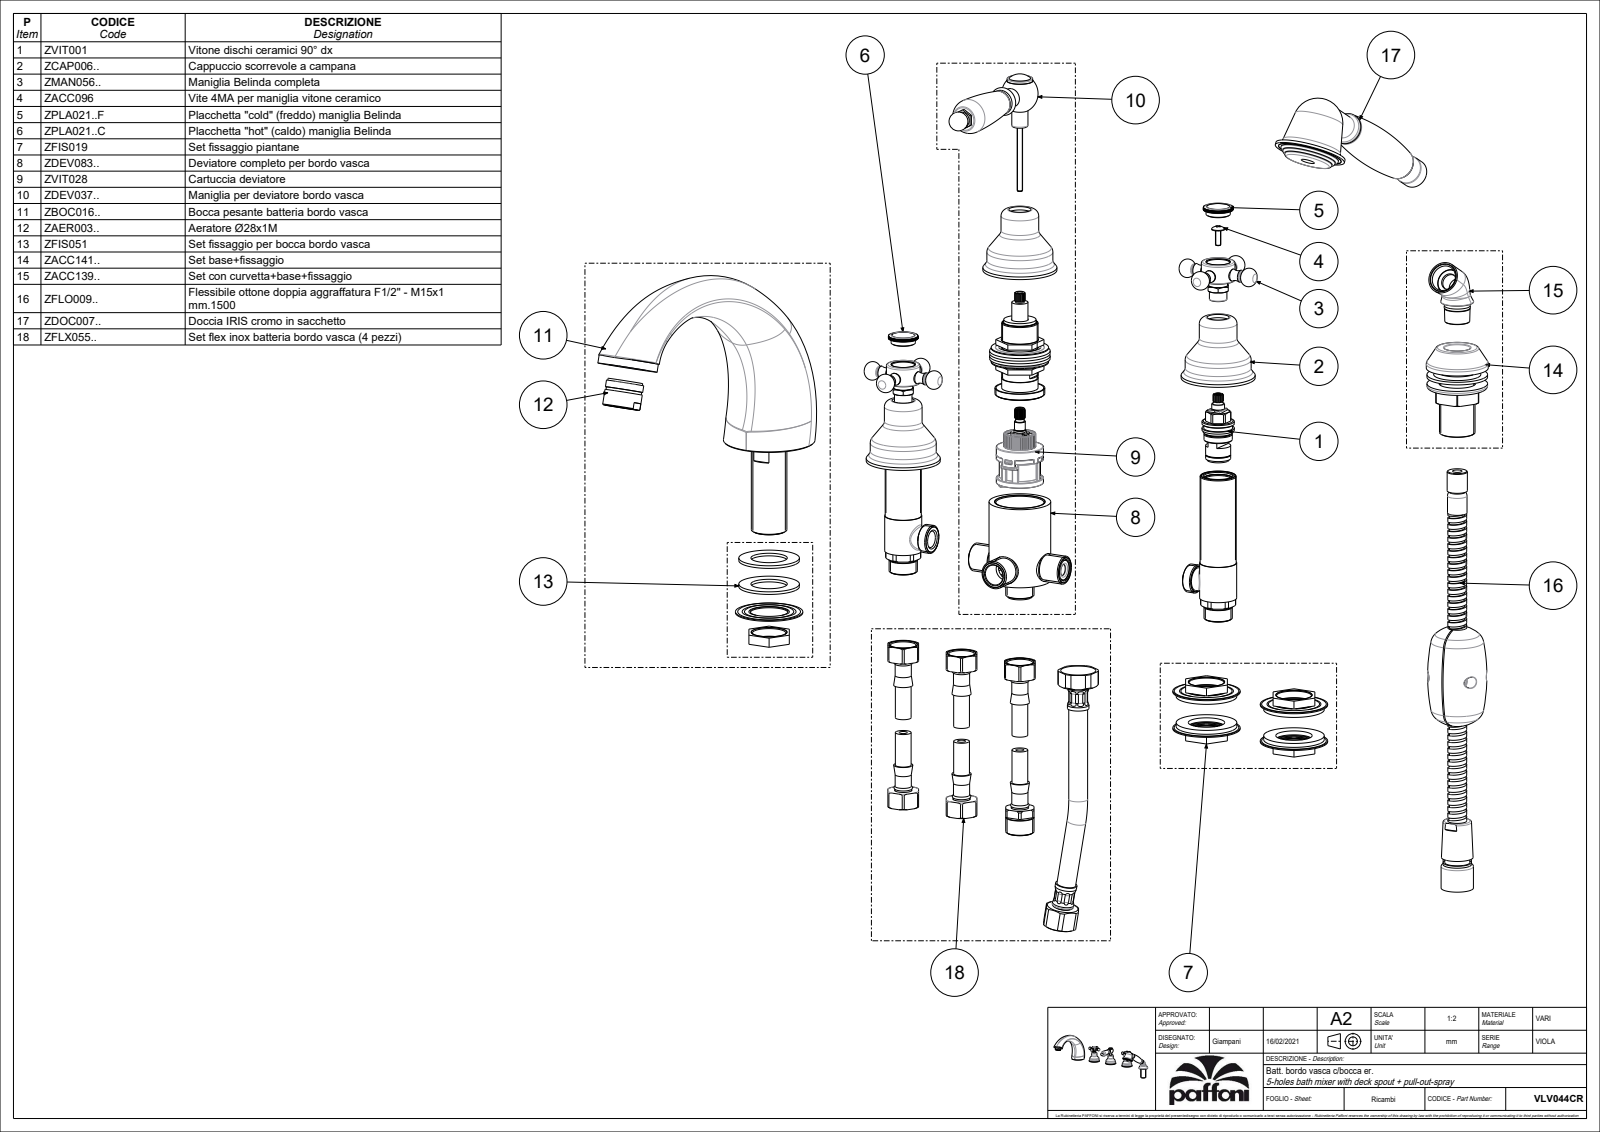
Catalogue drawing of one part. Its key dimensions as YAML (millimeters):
part_name: "VLV044CR"
step_written_by: "CREO PARAMETRIC BY PTC INC, 2020044 (CONFIG_CONTROL_DESIGN)"
units: millimeters
bodies: {solids: 5, faces: 1090, planar: 470, cylindrical: 320, other: 300}
overall_size: [460.5, 267.6, 150.84]
volume: 932553
surface_area: 131326
round_holes:
  - {diameter: 14.5, count: 1}
round_bosses_or_shafts:
  - {diameter: 28, count: 4}
  - {diameter: 14, count: 4}
  - {diameter: 55, count: 3}
  - {diameter: 49, count: 3}
  - {diameter: 9, count: 3}
  - {diameter: 7, count: 3}
  - {diameter: 25, count: 2}
  - {diameter: 13, count: 2}
partial_cylinders:
  - {radius: 11, count: 2}
face_to_face_distances: [6, 10, 60.1, 46.5, 13.6, 15, 2, 15.7, 30.8, 44.4]
